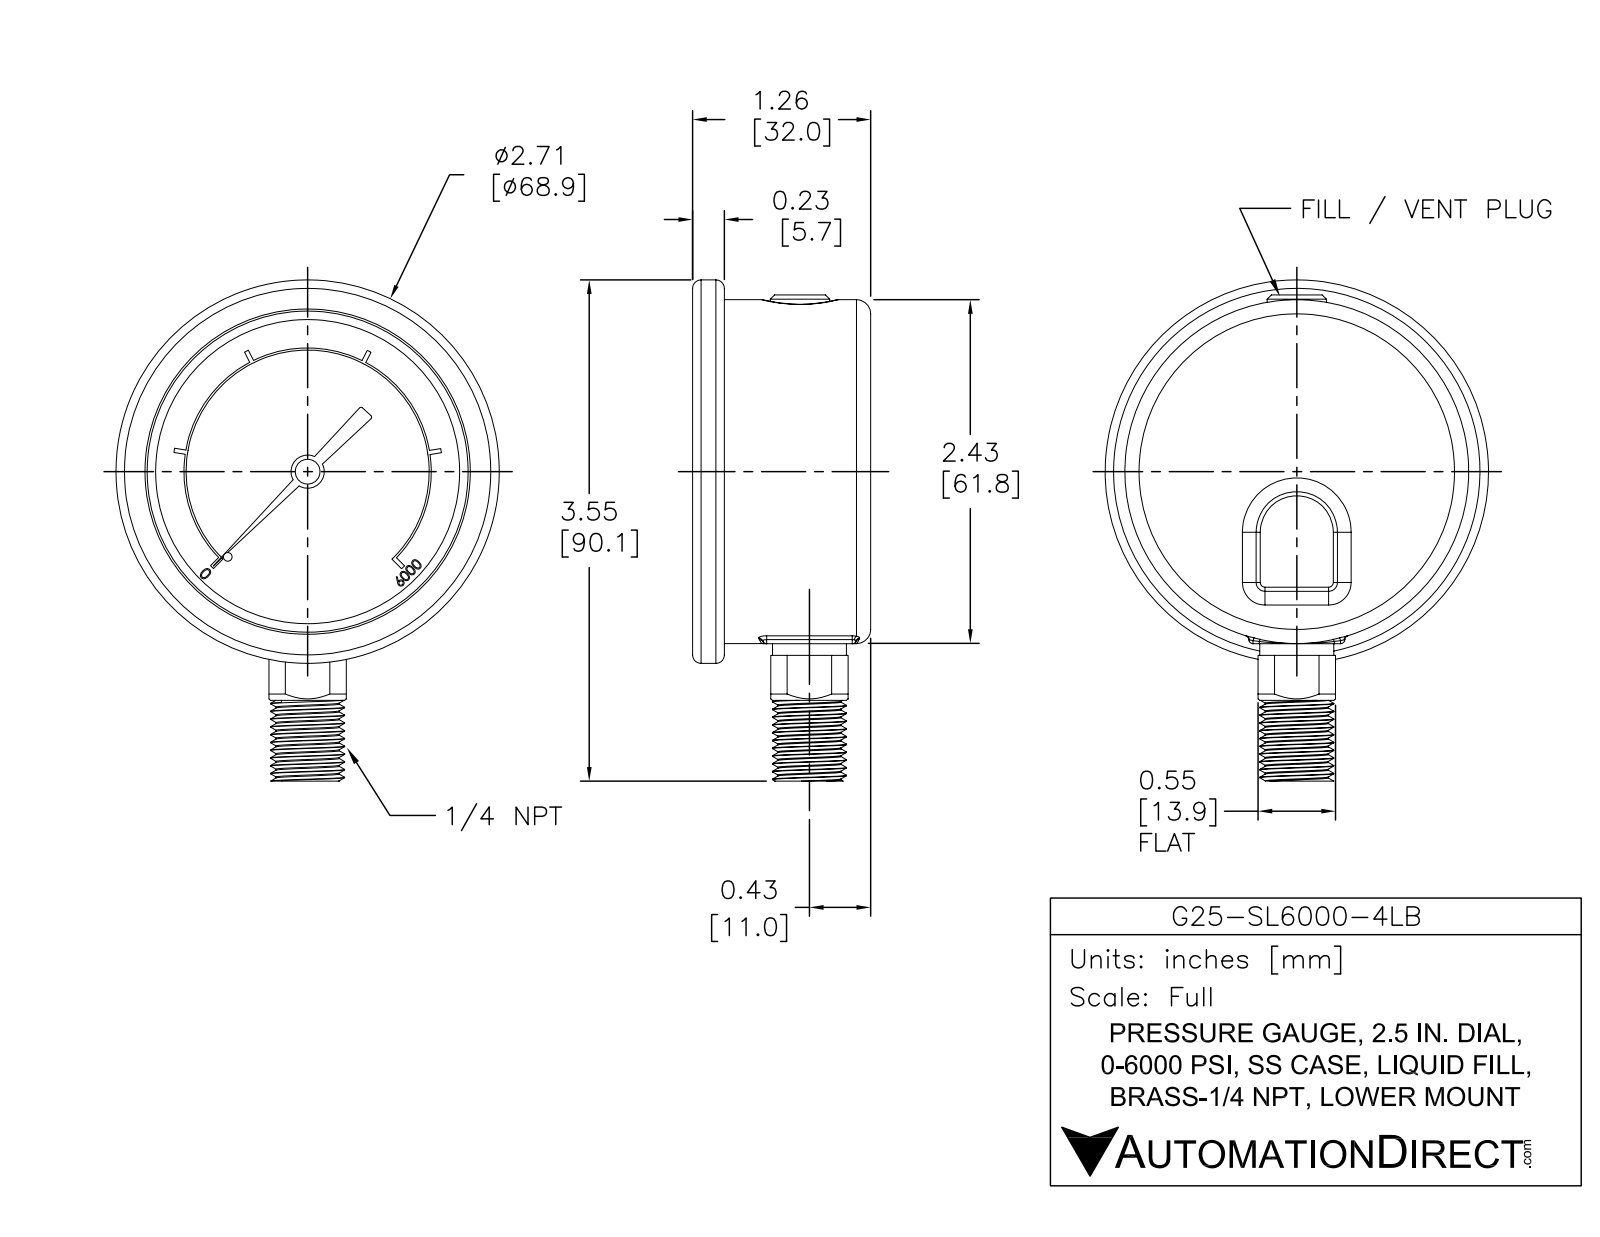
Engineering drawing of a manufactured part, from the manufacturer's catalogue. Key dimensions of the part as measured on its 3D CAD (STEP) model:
Part name (STEP PRODUCT): G25-SL6000-4LB
STEP written by: SolidWorks 2021 (AUTOMOTIVE_DESIGN)
Units: inches
Bodies: 1 solid, 361 faces (195 planar, 85 cylindrical, 81 other)
Overall size (bounding box): 3.546 × 2.713 × 1.26
Volume: 5.273 in³ · Surface area: 24.68 in²
Round holes (diameter × count): ⌀0.027 ×1, ⌀0.071 ×1, ⌀0.119 ×1, ⌀2.272 ×1
Round bosses / shafts (diameter × count): ⌀2.713 ×1, ⌀2.433 ×1, ⌀0.524 ×1, ⌀0.42 ×1, ⌀0.235 ×1, ⌀0.176 ×1, ⌀0.14 ×1, ⌀0.041 ×1
Partial cylindrical surfaces — rounded edges, fillets, slot ends (radius × count): R0.03 ×9, R0.1 ×3, R0.015 ×2, R0.316 ×1, R0.86 ×1, R0.875 ×1
Main face-to-face distances: 1.01, 1.26, 0.25, 1.035, 0.025, 0.225, 0.1, 0.91, 0.935, 1.16
Hole centre spacings: 0.067
